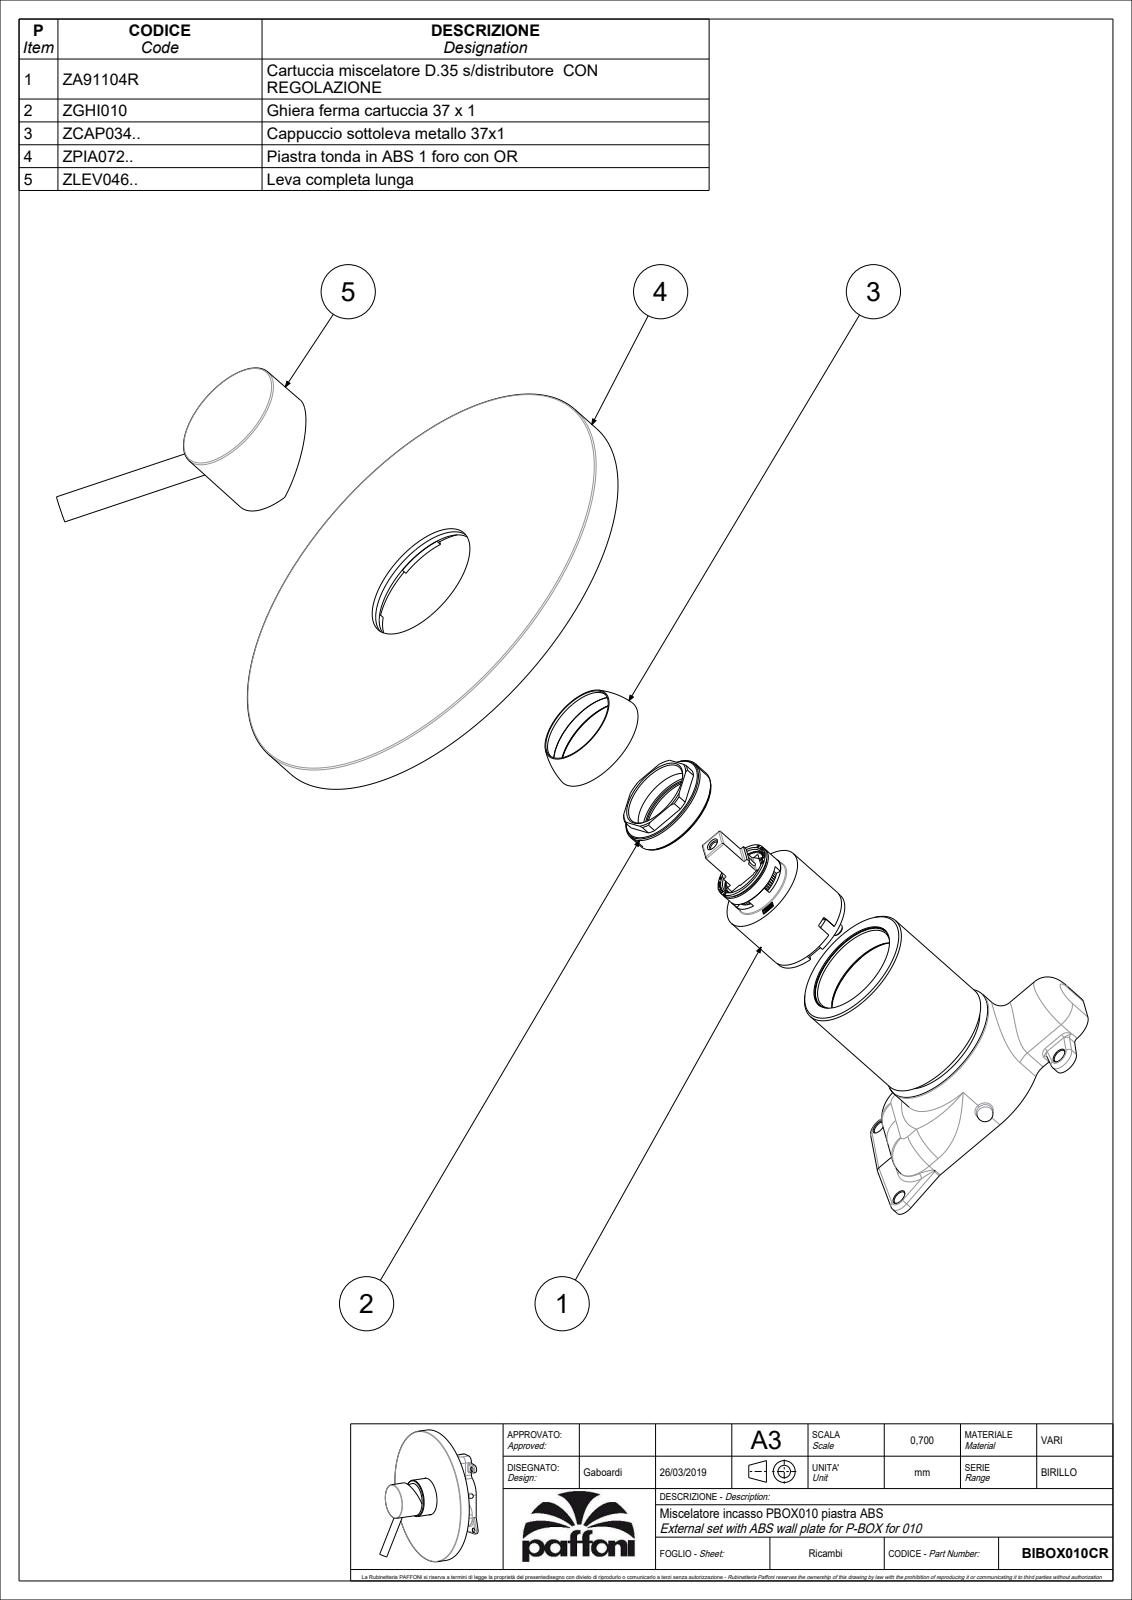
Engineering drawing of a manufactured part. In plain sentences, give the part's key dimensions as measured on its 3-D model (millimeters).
The part is named "BIBOX010CR". Its 3-D file was written by "CREO PARAMETRIC BY PTC INC, 2020044 (CONFIG_CONTROL_DESIGN)". It is 2 solids with 1035 faces: 591 planar, 245 cylindrical and 199 other. Overall it measures 173 by 173 by 84.91 millimeters. Its volume is 232 427 cubic millimeters and its surface area 100 323 square millimeters. Round holes: 3 of diameter 5, 3 of diameter 7, 2 of diameter 2, 2 of diameter 4, 1 of diameter 3.3, 1 of diameter 10, 1 of diameter 19.5, 1 of diameter 19.9, 1 of diameter 26.8, 1 of diameter 29, 1 of diameter 31, 1 of diameter 32.4. Round bosses or shafts: 2 of diameter 4.8, 1 of diameter 173, 1 of diameter 167, 1 of diameter 56.5, 1 of diameter 48.1, 1 of diameter 39, 1 of diameter 35, 1 of diameter 34.8. Partial cylindrical surfaces (rounded edges, fillets, slot ends): 51 of radius 0.5, 11 of radius 0.15, 4 of radius 0.3, 2 of radius 1, 1 of radius 2.5, 1 of radius 5, 1 of radius 7, 1 of radius 9.3. The main face-to-face distances are 13, 2, 11, 4.5, 6.5, 28.1, 4.2, 6.8, 6.2, 22. The hole center spacings are 8.6, 13.45, 15.13, 21.93, 14, 18.
